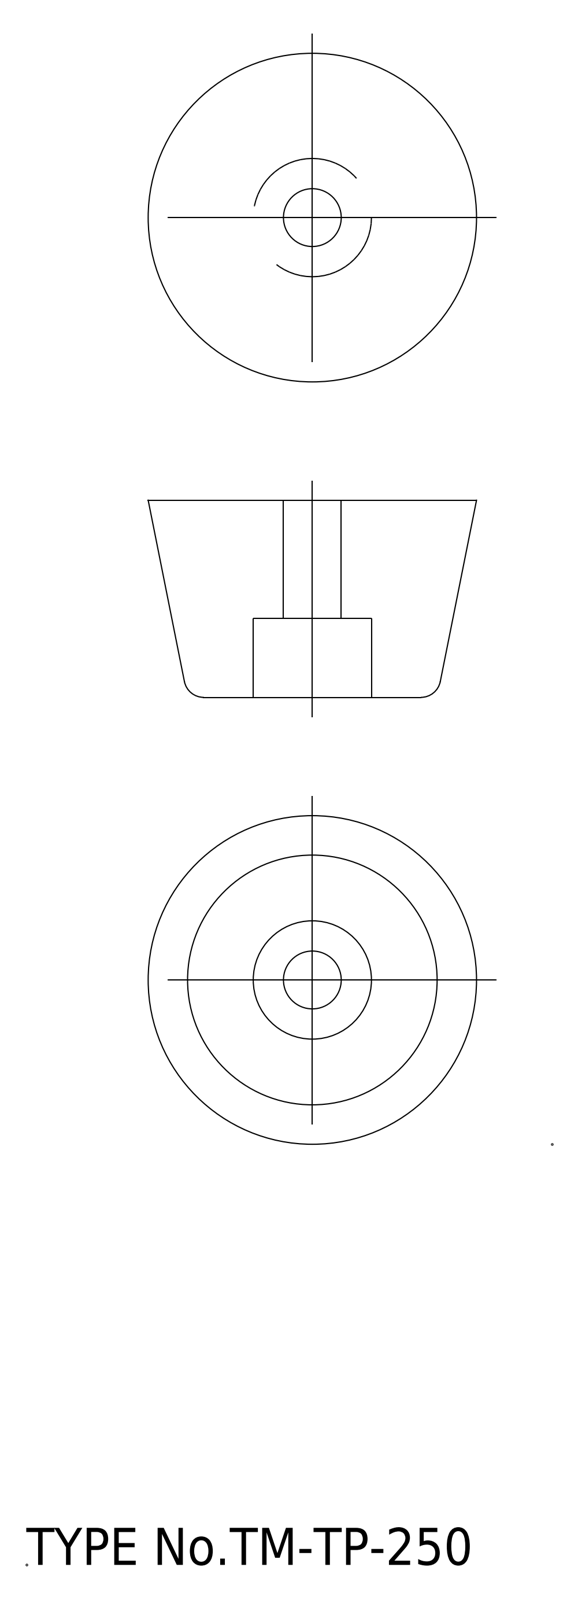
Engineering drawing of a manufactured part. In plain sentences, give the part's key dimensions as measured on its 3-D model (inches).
Its 3-D file was written by "spGate 19.8.4 (****-****-****-****) (AUTOMOTIVE_DESIGN)". It is 1 solid with 11 faces: 3 planar, 4 cylindrical and 4 other. Overall it measures 0.984 by 0.984 by 0.591 inches. Its volume is 0.318 cubic inches and its surface area 3.212 square inches. Round holes: 1 of diameter 0.173, 1 of diameter 0.354. The main face-to-face distances are 0.591, 0.236, 0.354.
